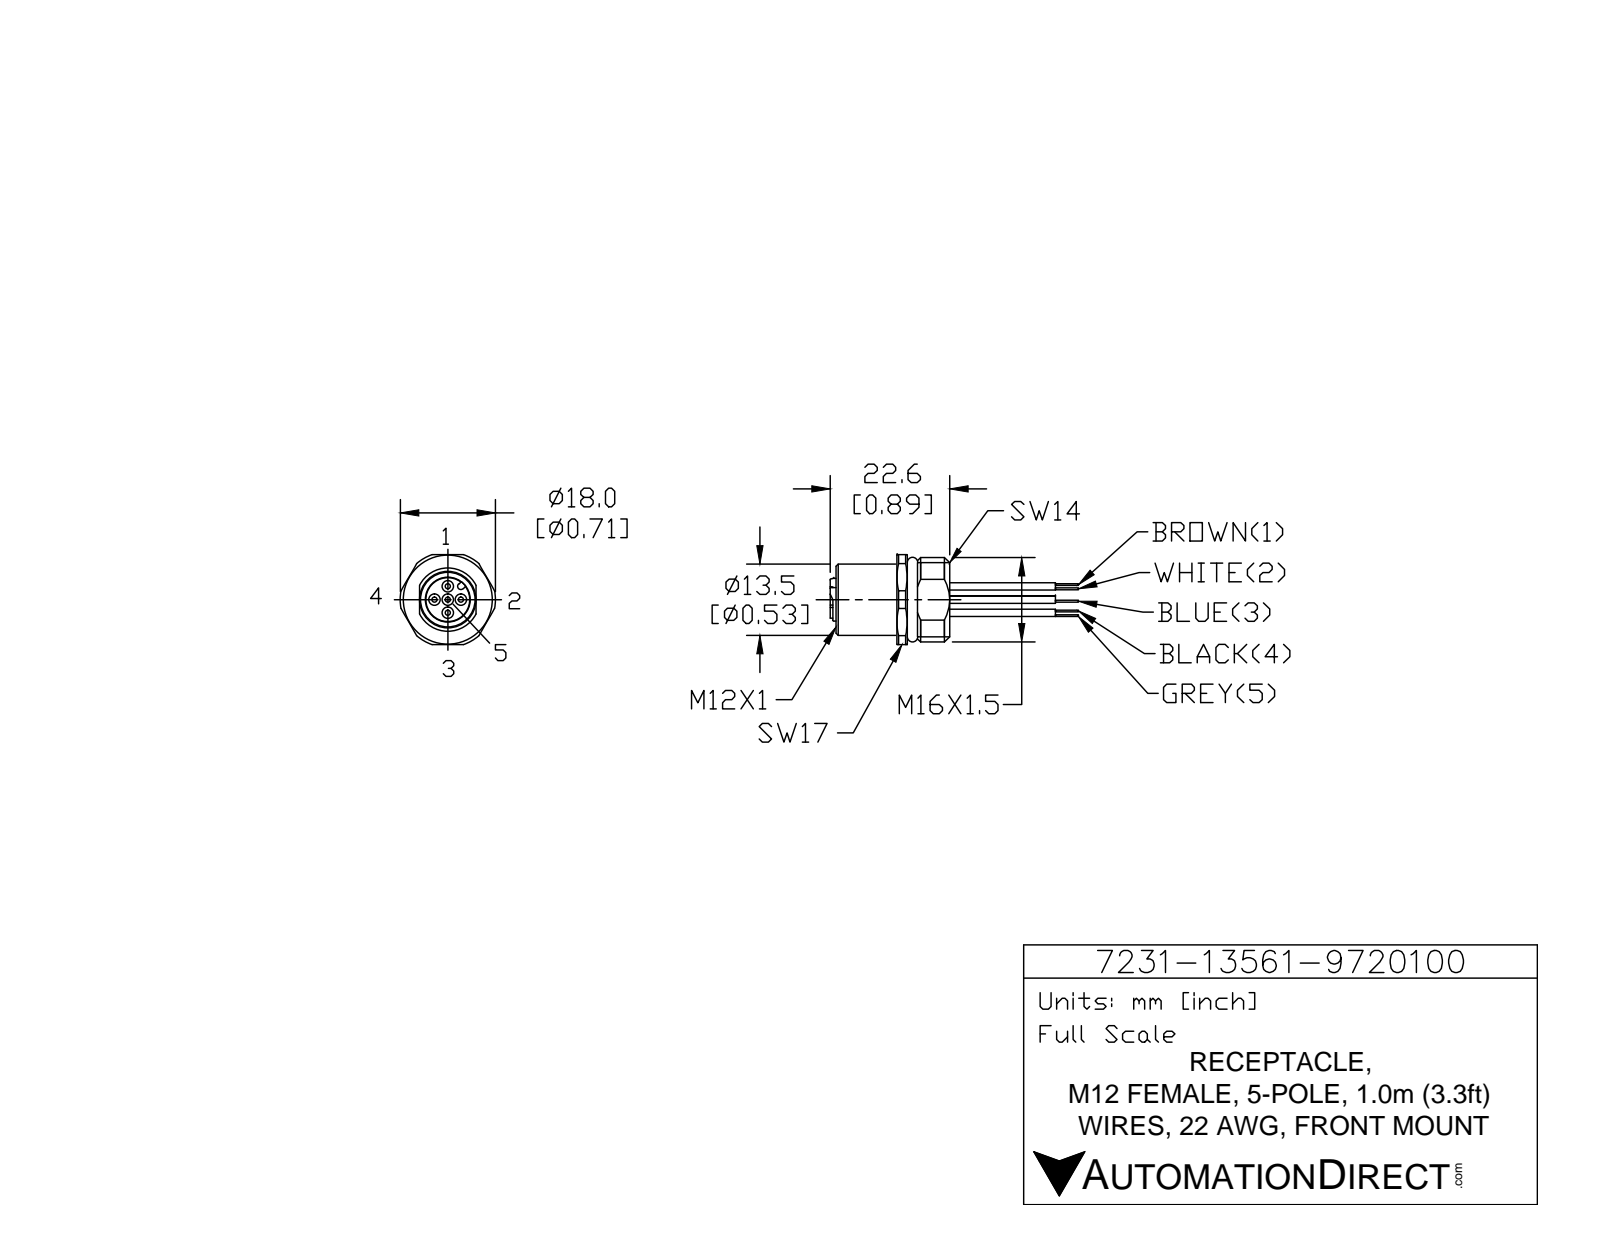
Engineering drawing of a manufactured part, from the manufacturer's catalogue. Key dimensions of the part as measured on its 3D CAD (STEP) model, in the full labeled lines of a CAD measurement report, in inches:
Part name (STEP PRODUCT): 7231-13561-9720100
STEP written by: SolidWorks 2015 (AUTOMOTIVE_DESIGN)
Units: inches
Bodies: 1 solid, 156 faces (39 planar, 65 cylindrical, 52 other)
Overall size (bounding box): 1.677 × 0.709 × 0.669
Volume: 0.206 in³ · Surface area: 3.968 in²
Round holes (diameter × count): ⌀0.043 ×5, ⌀0.43 ×1, ⌀0.48 ×1, ⌀0.512 ×1
Round bosses / shafts (diameter × count): ⌀0.079 ×5, ⌀0.055 ×5, ⌀0.531 ×1, ⌀0.319 ×1
Partial cylindrical surfaces — rounded edges, fillets, slot ends (radius × count): R0.008 ×6, R0.024 ×1, R0.315 ×1, R0.354 ×1
Main face-to-face distances: 0.276, 0.555, 0.354, 0.079, 0.28, 0.201, 0.551, 0.831, 0.039, 0.669
Hole centre spacings: 0.098, 0.139, 0.197, 0.098, 0.099
